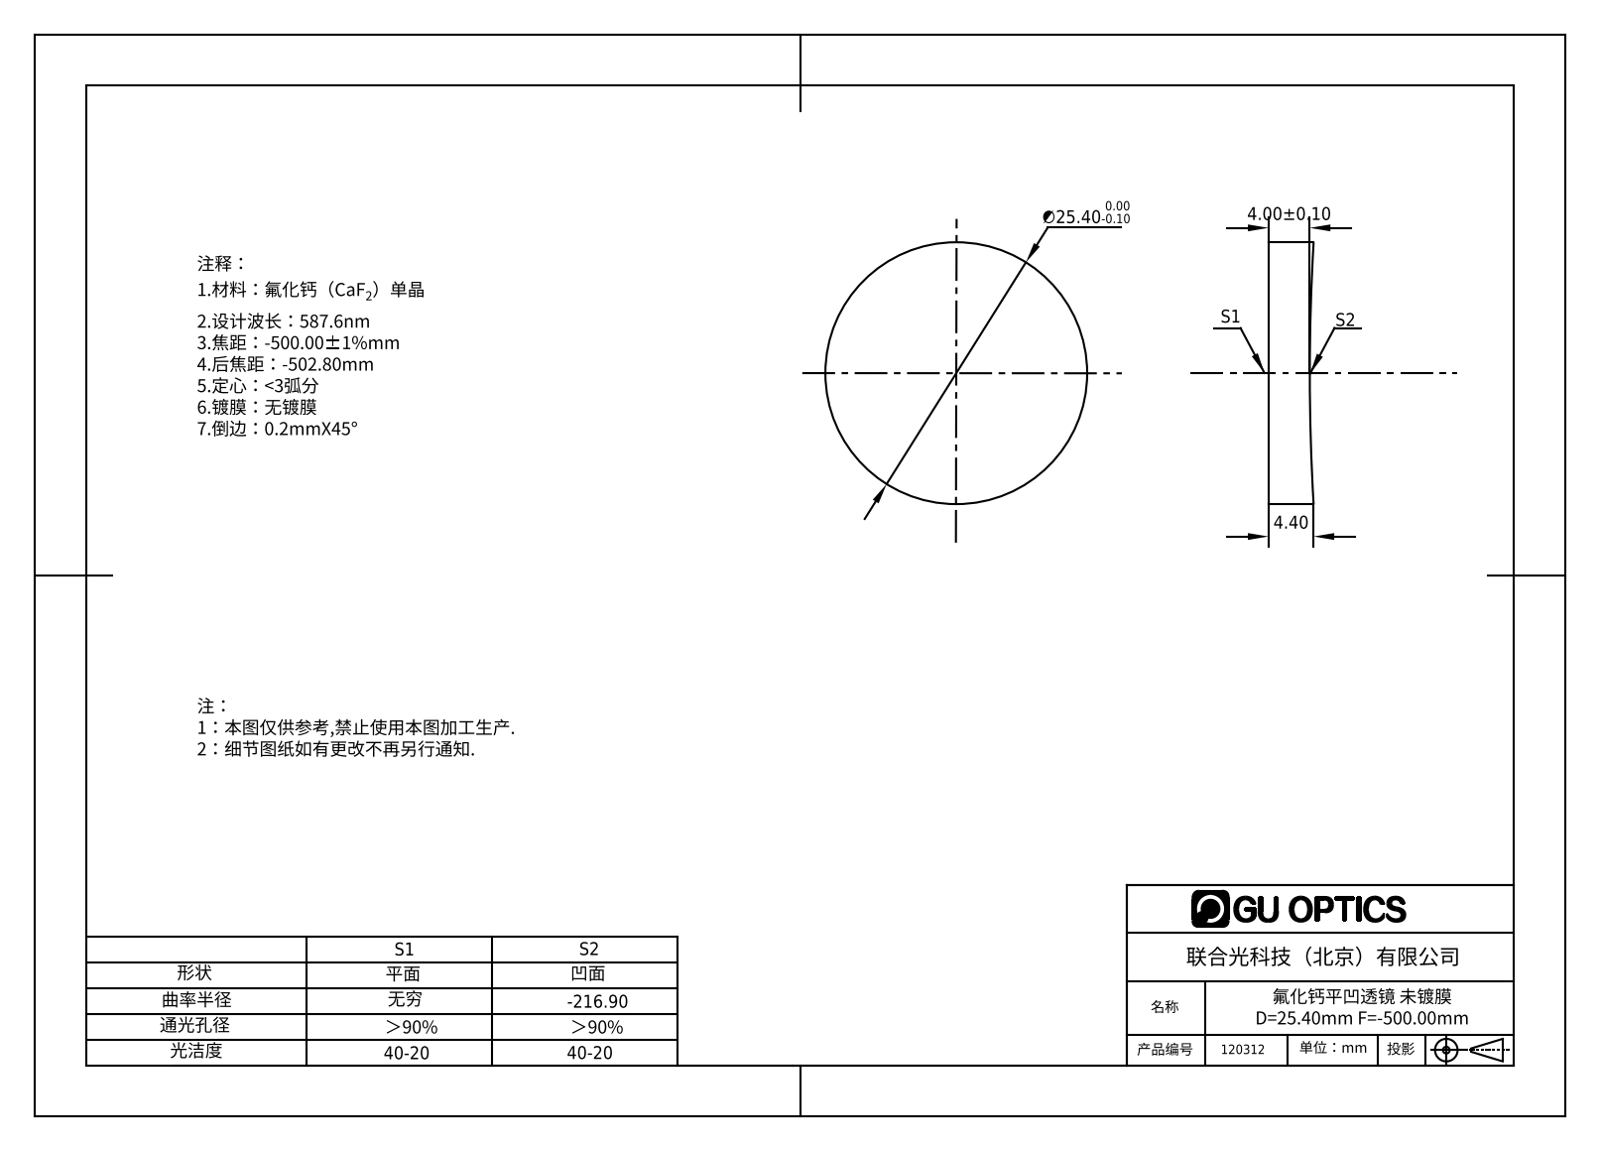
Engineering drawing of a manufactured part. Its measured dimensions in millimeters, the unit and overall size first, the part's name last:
Units: millimetres
Overall size (bounding box): 25.4 × 25.4 × 4.37
Round bosses / shafts (diameter × count): ⌀25.4 ×1
Volume: 2 121 mm³ · Surface area: 1 363 mm²
Bodies: 1 solid, 5 faces (1 planar, 2 cylindrical, 2 other)
Part name (STEP PRODUCT): 120312
STEP written by: SolidWorks 2016 (AUTOMOTIVE_DESIGN)
